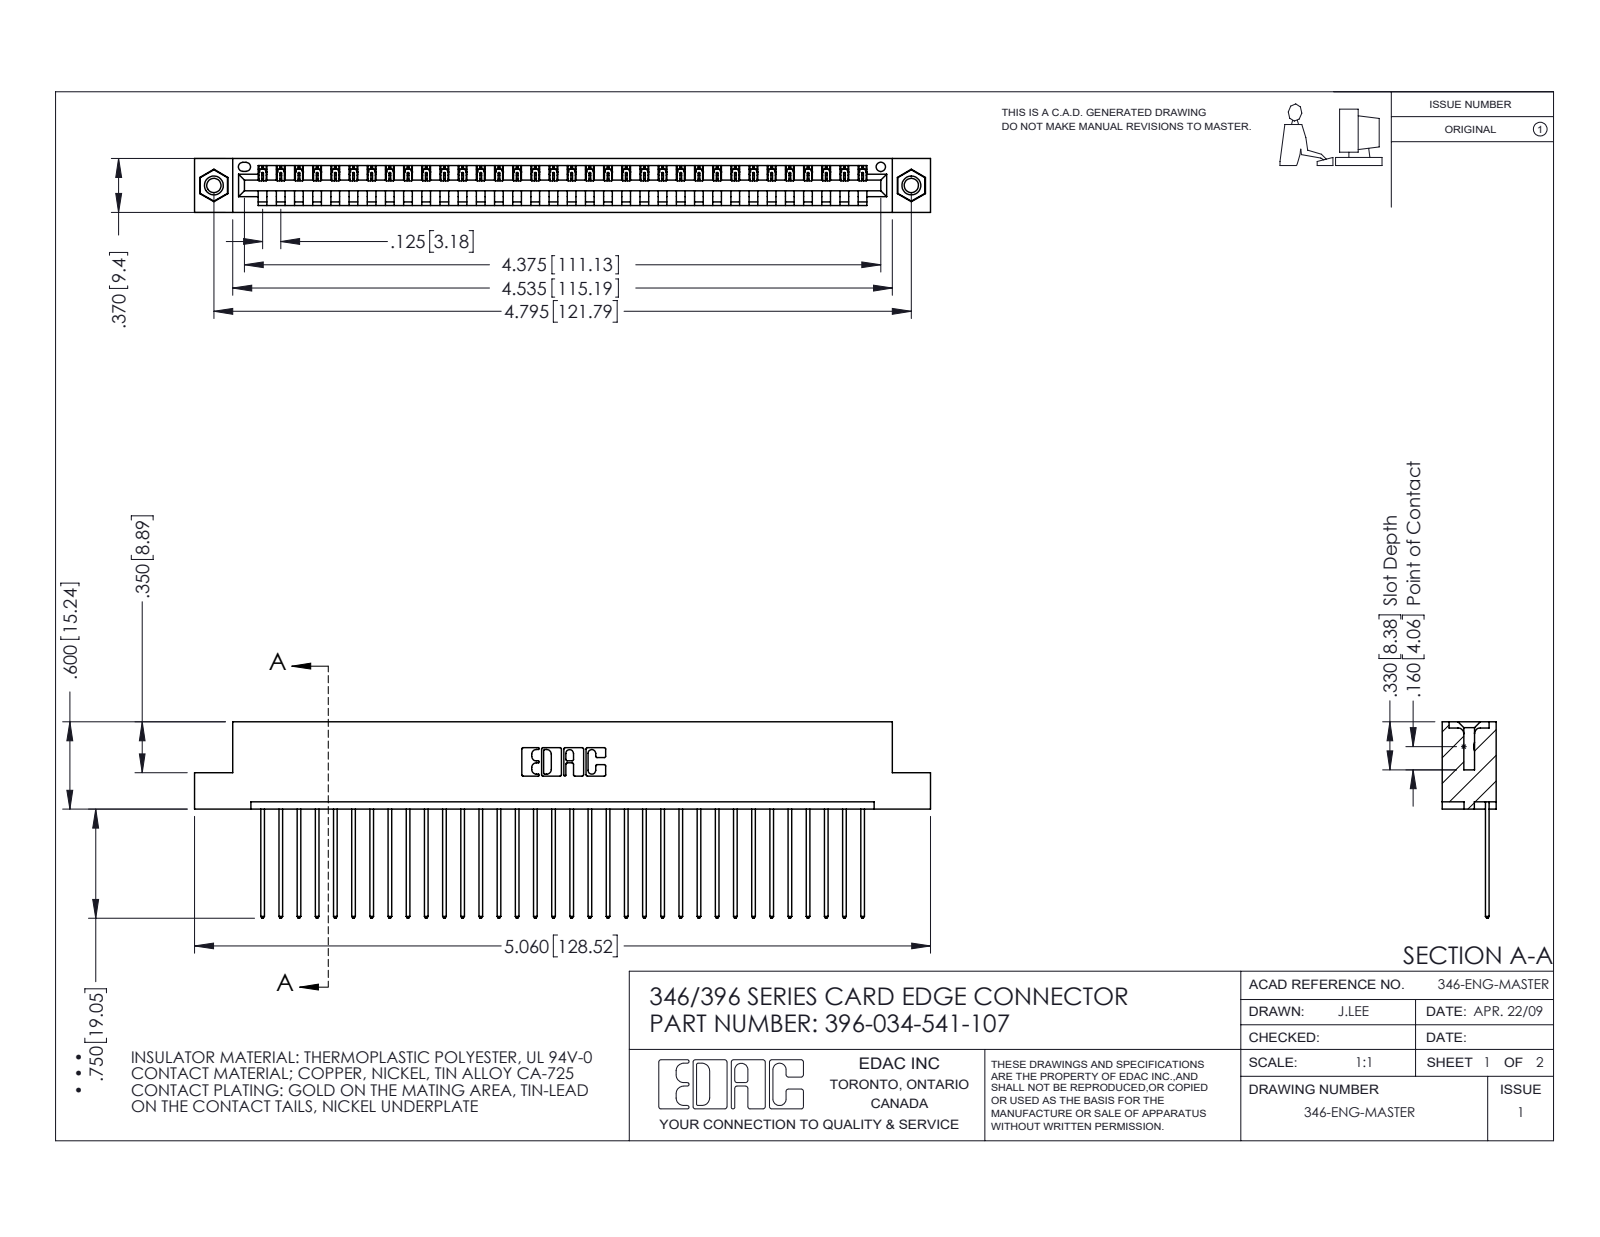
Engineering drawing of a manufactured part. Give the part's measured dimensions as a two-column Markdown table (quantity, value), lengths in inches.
| quantity | value |
| --- | --- |
| part name | 346 Part_Flush Mounting Lugs - 0.156 Dia-TI; 345-292-001_345-293-141; 396-034-541-107; 345-250-001_345-250-005-103 |
| STEP written by | SolidWorks 2016 (CONFIG_CONTROL_DESIGN) |
| units | inches |
| bodies | 37 solids, 2154 faces (1468 planar, 670 cylindrical, 16 other) |
| overall size | 5.06 × 1.35 × 0.37 |
| volume | 0.753 in³ |
| surface area | 24.88 in² |
| round holes (diameter × count) | 0.098 × 2, 0.125 × 2, 0.156 × 2, 0.064 × 1 |
| round bosses / shafts (diameter × count) | 0.155 × 2 |
| partial cylindrical surfaces (radius × count) | 0.006 × 68, 0.01 × 68, 0.01 × 22, 0.007 × 6, 0.031 × 6, 0.026 × 3, 0.031 × 2, 0.04 × 2 |
| main face-to-face distances | 0.048, 0.322, 0.37, 0.25, 0.072, 0.298, 0.025, 0.148, 0.222, 0.1 |
| hole center spacings | 0.246, 4.587, 4.795 |
